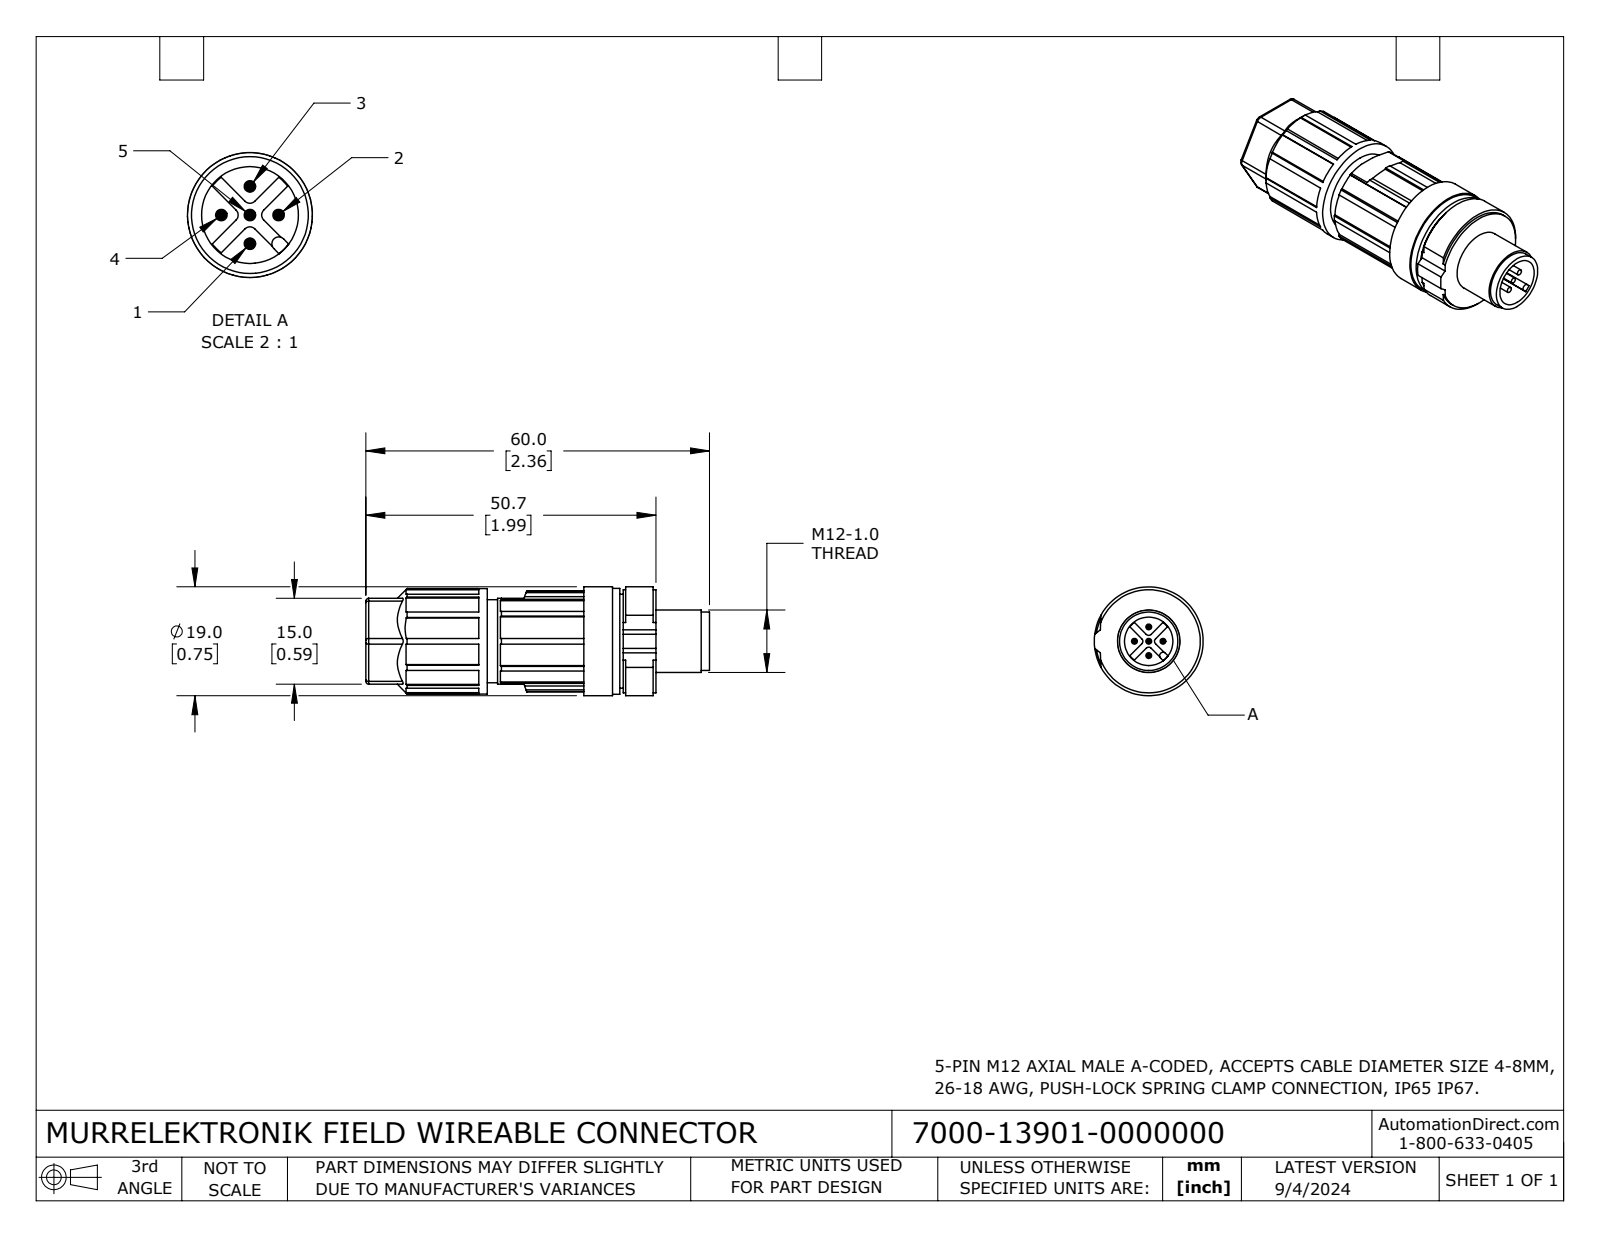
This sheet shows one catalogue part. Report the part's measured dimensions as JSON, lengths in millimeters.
{"part_name": "7000-13901-0000000", "step_written_by": "SolidWorks 2023 (CONFIG_CONTROL_DESIGN)", "units": "millimeters", "bodies": {"solids": 1, "faces": 204, "planar": 103, "cylindrical": 89, "other": 12}, "overall_size": [60, 19, 19], "volume_mm3": 10900, "surface_area_mm2": 5235, "round_holes": [[8.5, 1], [8.5, 1], [9, 1]], "round_bosses_or_shafts": [[1, 5], [19, 1], [18.5, 1], [18.4, 1], [18, 1], [16.4, 1], [14.5, 1], [10.9, 1]], "partial_cylinders_radius": [[0.5, 6], [1, 6], [0.6, 1], [4.2, 1], [8.5, 1], [8.8, 1]], "face_to_face_distances": [15, 6.3, 21.2, 29.4, 29, 50.6, 16, 5.7, 12.6, 1]}
